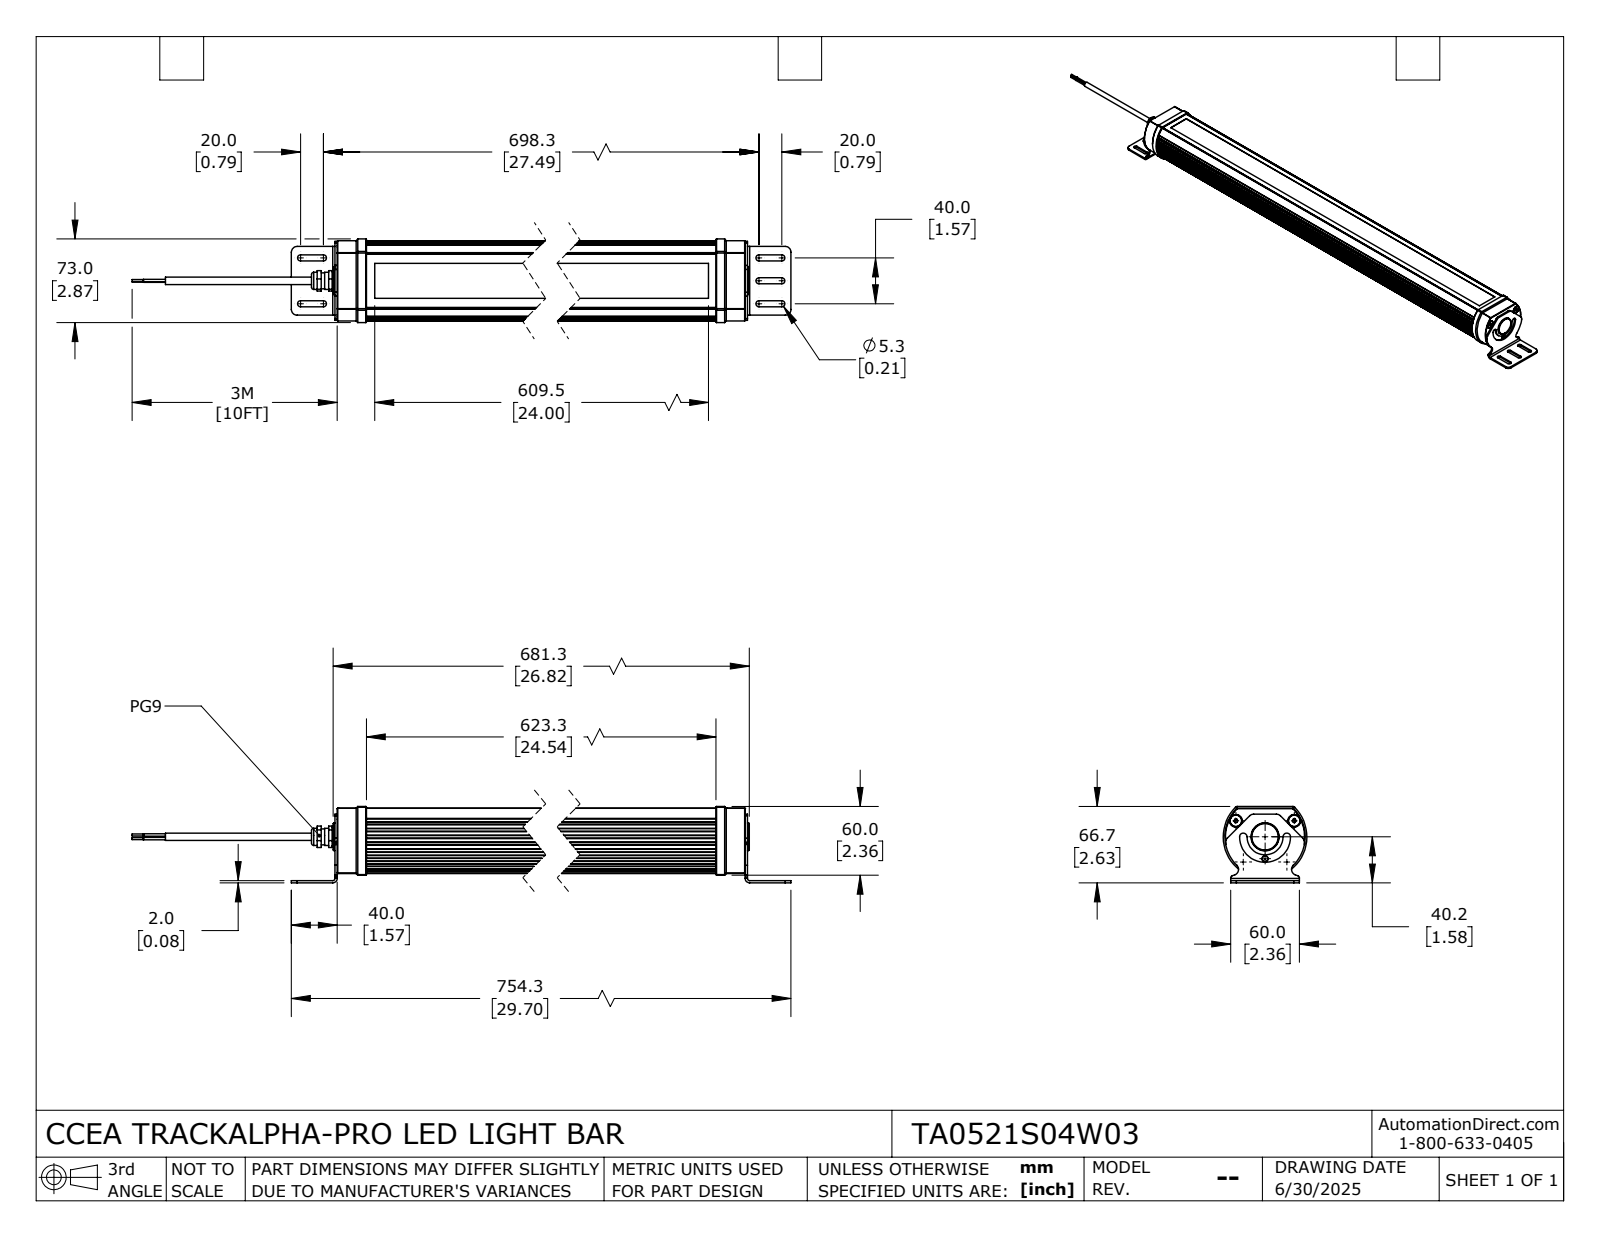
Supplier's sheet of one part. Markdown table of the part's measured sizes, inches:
| quantity | value |
| --- | --- |
| part name | TA0521S04W03 |
| STEP written by | SolidWorks 2024 (CONFIG_CONTROL_DESIGN) |
| units | inches |
| bodies | 3 solids, 695 faces (238 planar, 331 cylindrical, 126 other) |
| overall size | 35.169 × 2.874 × 2.626 |
| volume | 140 in³ |
| surface area | 379.2 in² |
| round holes (diameter × count) | 0.217 × 4, 0.043 × 2, 0.12 × 2, 0.394 × 2, 0.194 × 1, 0.276 × 1, 0.551 × 1, 0.965 × 1, 1.063 × 1 |
| round bosses / shafts (diameter × count) | 0.394 × 4, 0.197 × 4, 0.118 × 2, 0.082 × 2, 0.067 × 2, 0.063 × 2, 0.039 × 2, 0.945 × 1 |
| partial cylindrical surfaces (radius × count) | 0.02 × 22, 0.012 × 16, 0.197 × 13, 0.104 × 12, 0.059 × 10, 0.073 × 8, 0.079 × 8, 0.028 × 2 |
| main face-to-face distances | 2.24, 0.197, 0.02, 2.043, 2.242, 0.199, 0.217, 2.024, 0.219, 0.079 |
| hole center spacings | 0.334, 0.505, 0.726, 0.757, 0.831, 0.948, 0.992, 1.144 |
